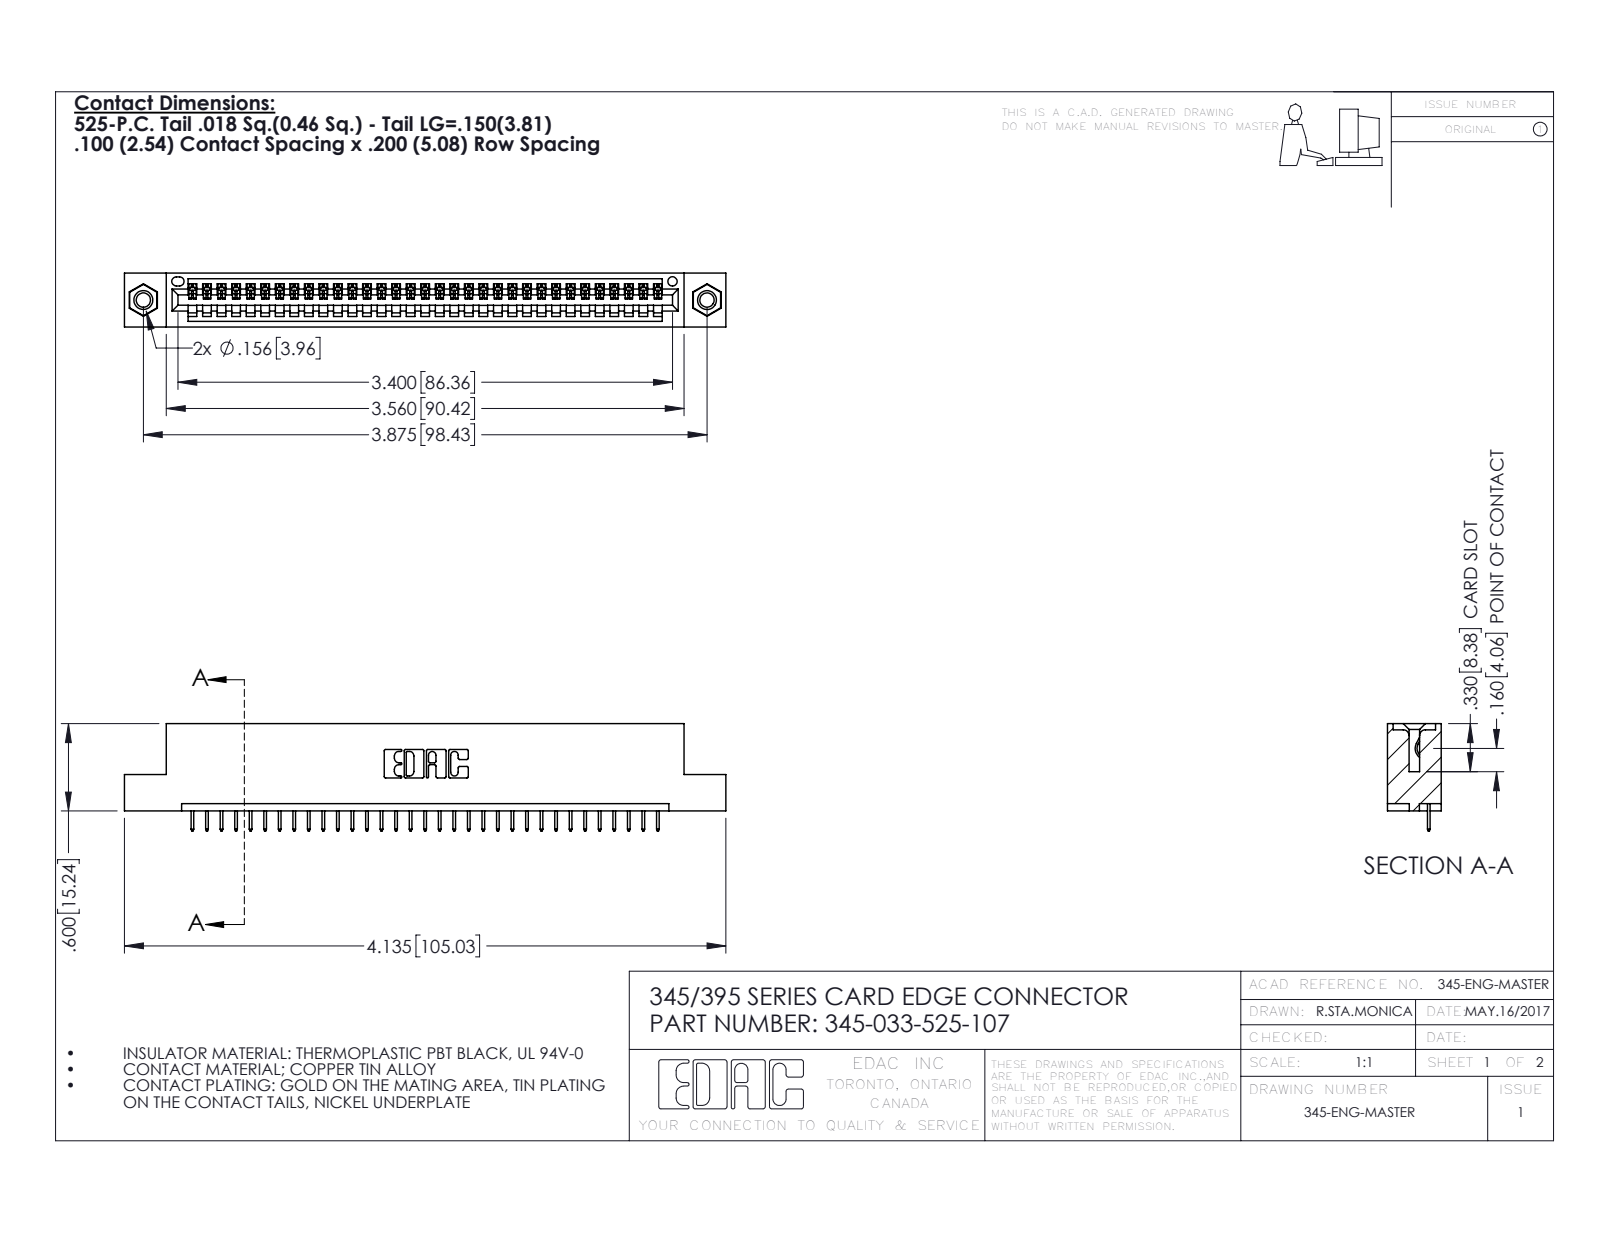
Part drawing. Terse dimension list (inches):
name: 345-033-525-107; 345 Part_Flush Mounting Lugs - 0.156 Dia-TI; 345-292-001_345-293-125; 345-250-001_345-250-005-103
written by: SolidWorks 2020 (CONFIG_CONTROL_DESIGN)
unit: in
bodies: 36 solids, 2232 faces (1630 planar, 586 cylindrical, 16 other)
size: 4.135 × 0.737 × 0.37
volume: 0.595 in³; area: 19.26 in²
holes: 2× ⌀0.098, 2× ⌀0.125, 2× ⌀0.156, 1× ⌀0.064
bosses: 2× ⌀0.155
rounds: 66× R0.006, 22× R0.01, 6× R0.007, 6× R0.031, 3× R0.026, 2× R0.031, 2× R0.04, 1× R0.014
face distances: 0.072, 0.298, 0.37, 0.2, 0.098, 0.272, 0.025, 0.225, 0.072, 0.149
hole spacings: 0.27, 3.64, 3.875
